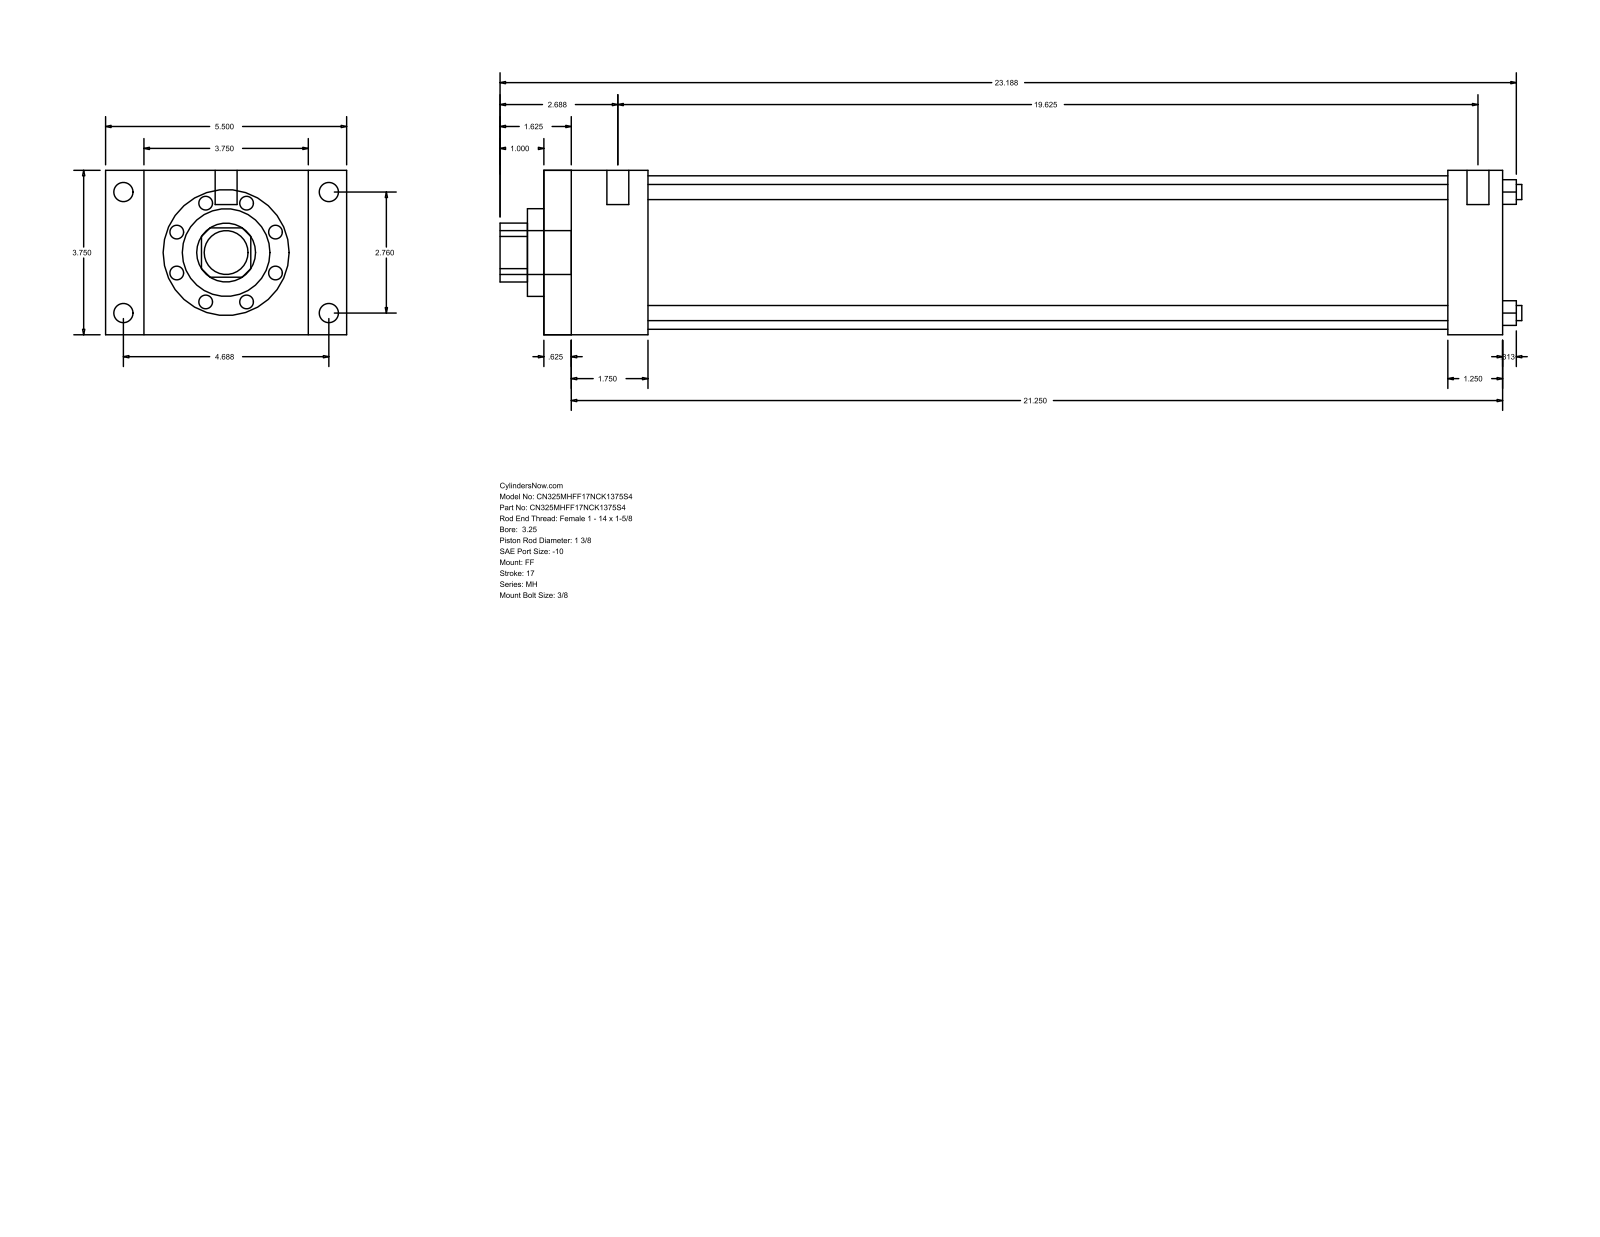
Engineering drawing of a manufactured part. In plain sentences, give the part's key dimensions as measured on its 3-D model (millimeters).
The part is named "MH_FF__0325_1.375". Its 3-D file was written by "GSSL Pune (CONFIG_CONTROL_DESIGN)". It is 0 solids with 92 faces: 64 planar, 28 cylindrical and 0 other. Overall it measures 592.14 by 139.7 by 95.25 millimeters. Round holes: 4 of diameter 8.76, 1 of diameter 34.92, 1 of diameter 50.8, 1 of diameter 88.9. Round bosses or shafts: 4 of diameter 11.13, 4 of diameter 5.56, 2 of diameter 12.7, 1 of diameter 25.4. Partial cylindrical surfaces (rounded edges, fillets, slot ends): 1 of radius 17.06. The main face-to-face distances are 95.24, 555.62, 15.87, 539.75, 22.23, 117.47, 523.87, 508, 31.75, 60.32. The hole center spacings are 49.57, 70.1, 99.14.
